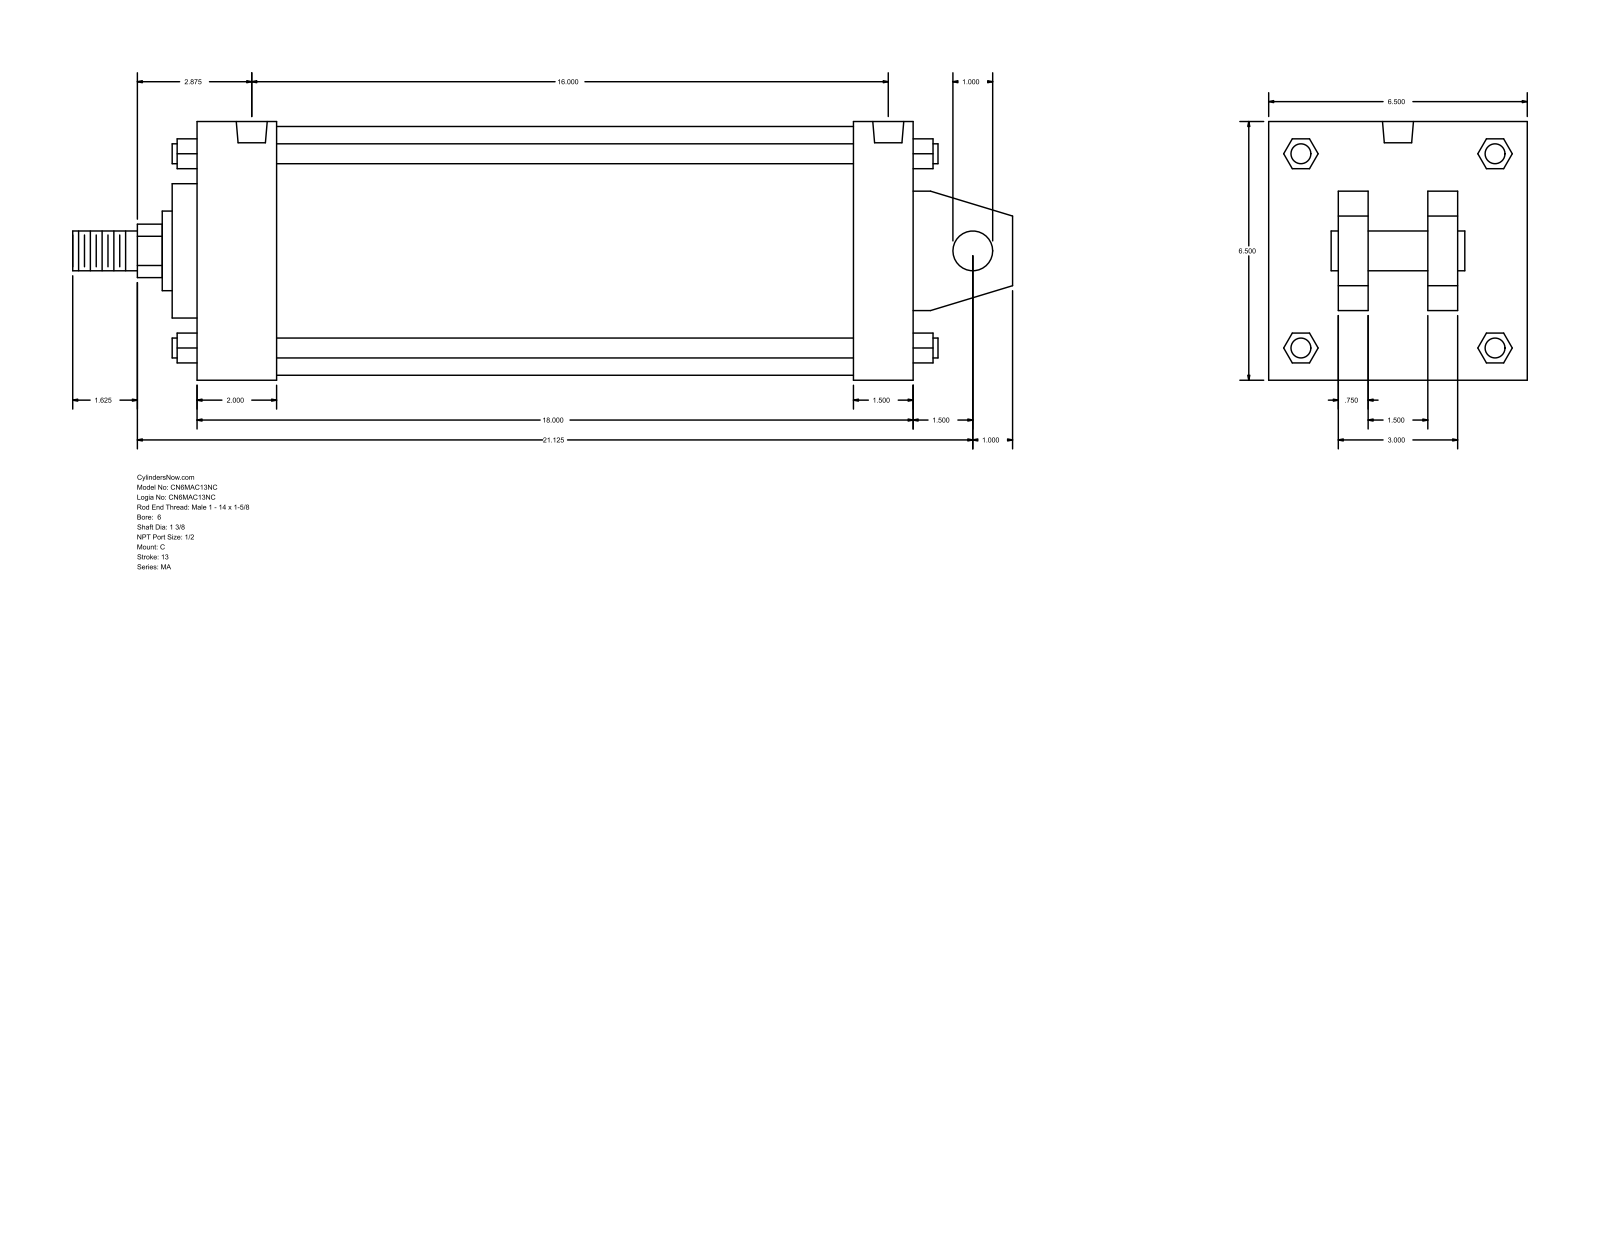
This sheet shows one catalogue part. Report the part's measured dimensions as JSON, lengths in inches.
{"part_name": "MA_C__0600_1.375", "step_written_by": "GSSL Pune (CONFIG_CONTROL_DESIGN)", "units": "inches", "bodies": {"solids": 0, "faces": 141, "planar": 109, "cylindrical": 32, "other": 0}, "overall_size": [23.625, 6.5, 6.5], "round_holes": [[0.687, 4], [0.778, 2]], "round_bosses_or_shafts": [[0.5, 4], [1, 2], [6.25, 1], [3.375, 1], [2, 1], [1.375, 1]], "partial_cylinders_radius": [[0.672, 1]], "face_to_face_distances": [6.5, 18, 1.5, 0.75, 2.5, 4, 2, 1.75, 4.75, 16.5], "hole_center_spacings": [16, 0.125, 15.875, 16.125]}
